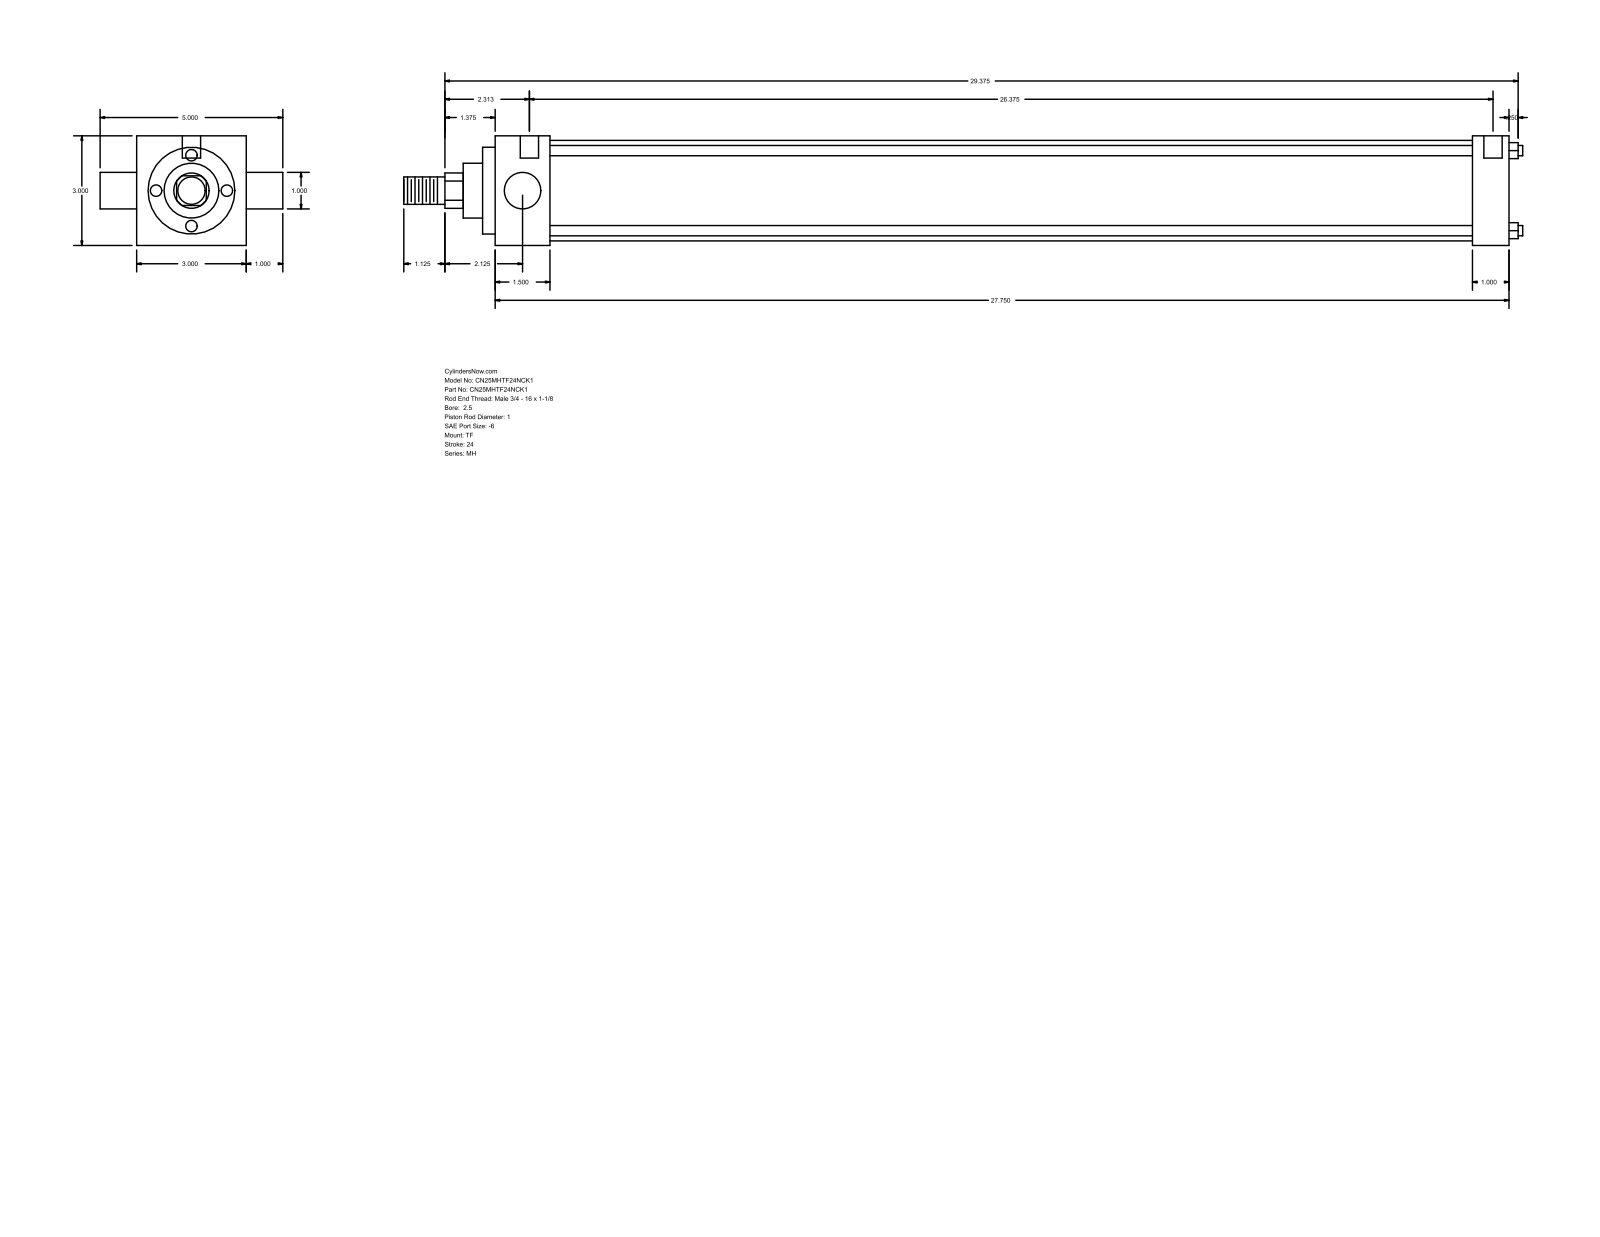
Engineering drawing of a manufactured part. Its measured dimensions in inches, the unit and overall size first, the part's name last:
Units: inches
Overall size (bounding box): 30.625 × 5 × 3
Round holes (diameter × count): ⌀0.219 ×3, ⌀0.5 ×2
Round bosses / shafts (diameter × count): ⌀0.281 ×4, ⌀1 ×2, ⌀2.75 ×1, ⌀2.375 ×1, ⌀1.5 ×1, ⌀0.75 ×1
Partial cylindrical surfaces — rounded edges, fillets, slot ends (radius × count): R0.484 ×1
Main face-to-face distances: 3, 27.75, 1, 1.5, 26.25, 26.75, 25.25, 0.344, 1.844, 27.094
Hole centre spacings: 0.125, 0.187, 26.375, 26.5, 26.562, 26.687
Bodies: 0 solids, 86 faces (61 planar, 25 cylindrical, 0 other)
Part name (STEP PRODUCT): MH_TF__0250_1
STEP written by: GSSL Pune (CONFIG_CONTROL_DESIGN)
